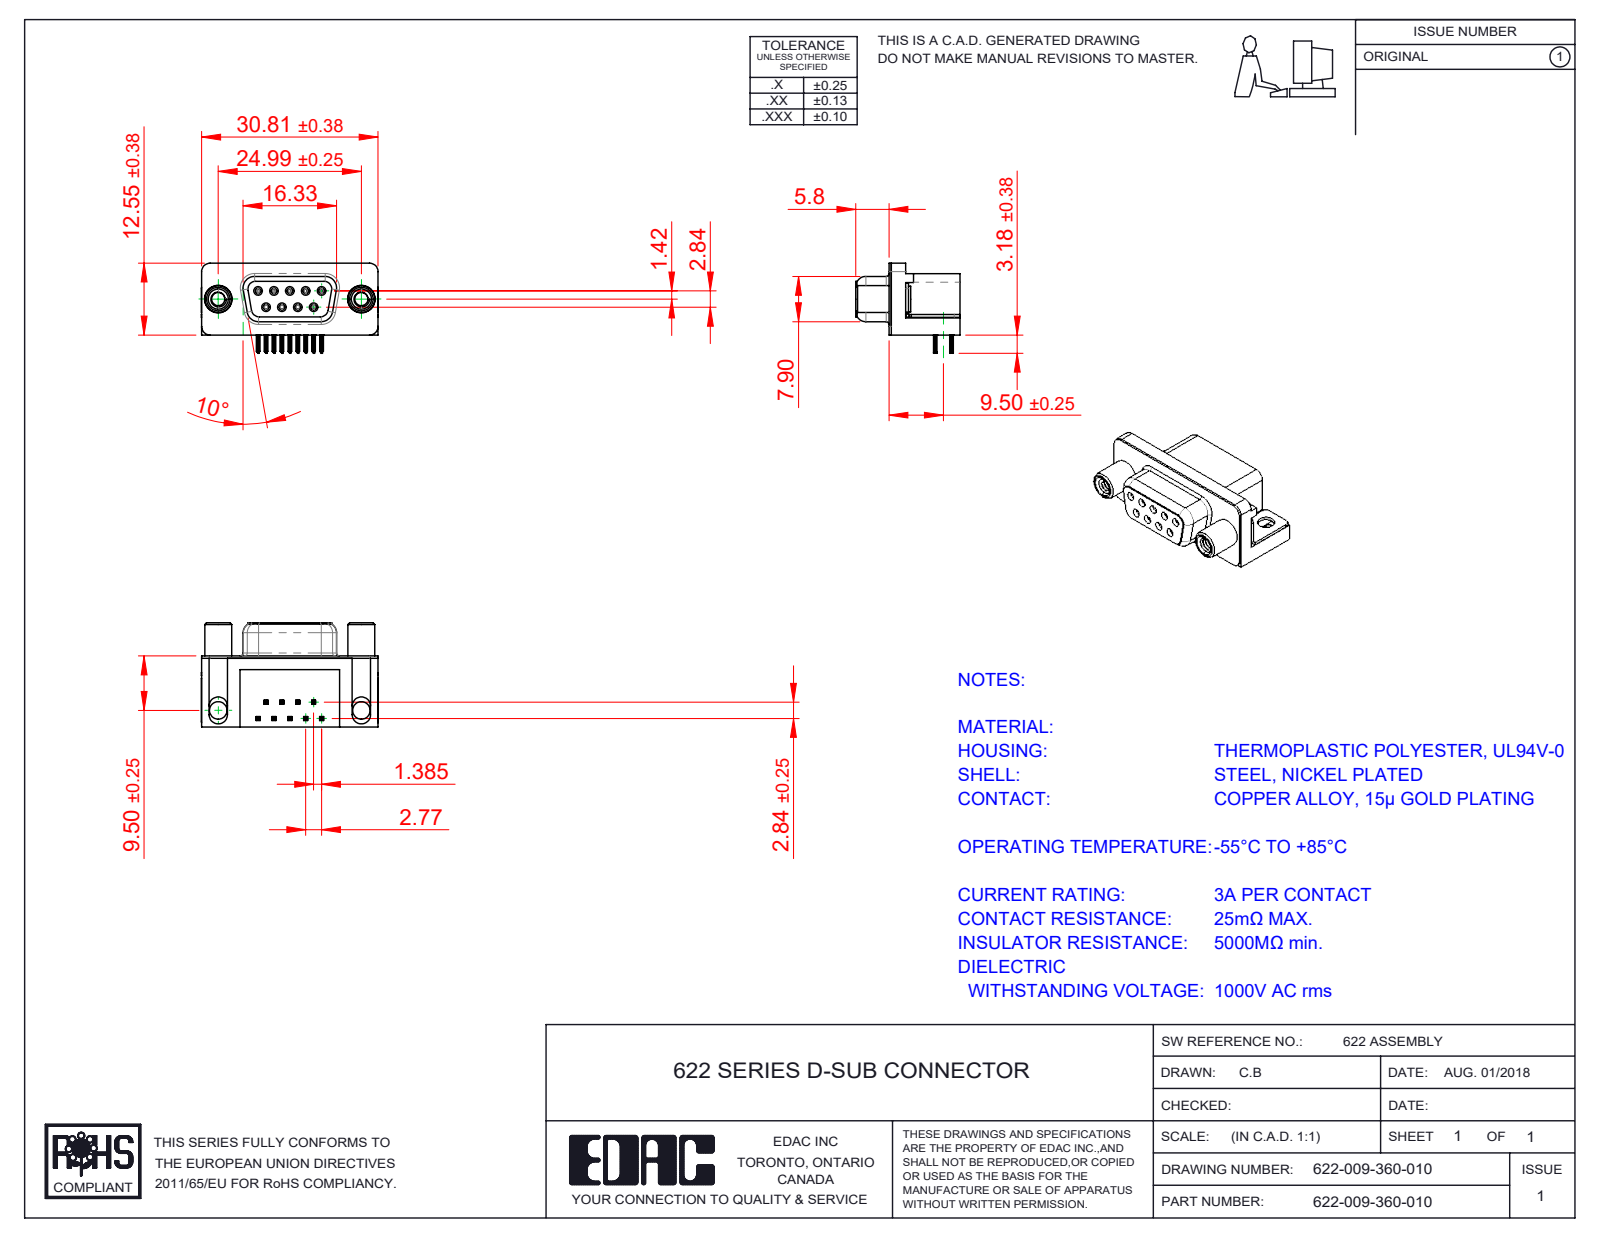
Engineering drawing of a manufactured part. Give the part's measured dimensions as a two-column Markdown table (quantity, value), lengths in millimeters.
| quantity | value |
| --- | --- |
| part name | 622 Round Threaded Standoff; 622-009-360-010; 622 Socket Bottom; 622 Housing_9 Socket (+3 more) |
| STEP written by | SolidWorks 2016 (CONFIG_CONTROL_DESIGN) |
| units | millimeters |
| bodies | 15 solids, 1564 faces (674 planar, 424 cylindrical, 466 other) |
| overall size | 30.89 × 18.2 × 15.73 |
| volume | 3 814 mm³ |
| surface area | 5 260 mm² |
| round holes (diameter × count) | 0.8 × 9, 0.9 × 9, 2.3 × 2, 3.05 × 2, 3.1 × 2, 4 × 2, 4.8 × 2, 5 × 2 |
| round bosses / shafts (diameter × count) | 1.2 × 9, 4.9 × 2, 4.7 × 2, 4.5 × 2, 3.85 × 2 |
| partial cylindrical surfaces (radius × count) | 0.1 × 72, 0.15 × 36, 0.35 × 18, 1 × 18, 0.34 × 9, 1.35 × 8, 1.6 × 8, 1.5 × 7 |
| main face-to-face distances | 0.4, 12, 12.4, 0.35, 2.9, 2.5, 10.34, 5.8, 9.5, 6.2 |
| hole center spacings | 3.16, 2.77, 5.54, 5.03, 5.04, 8.31, 7.48, 7.49 |
